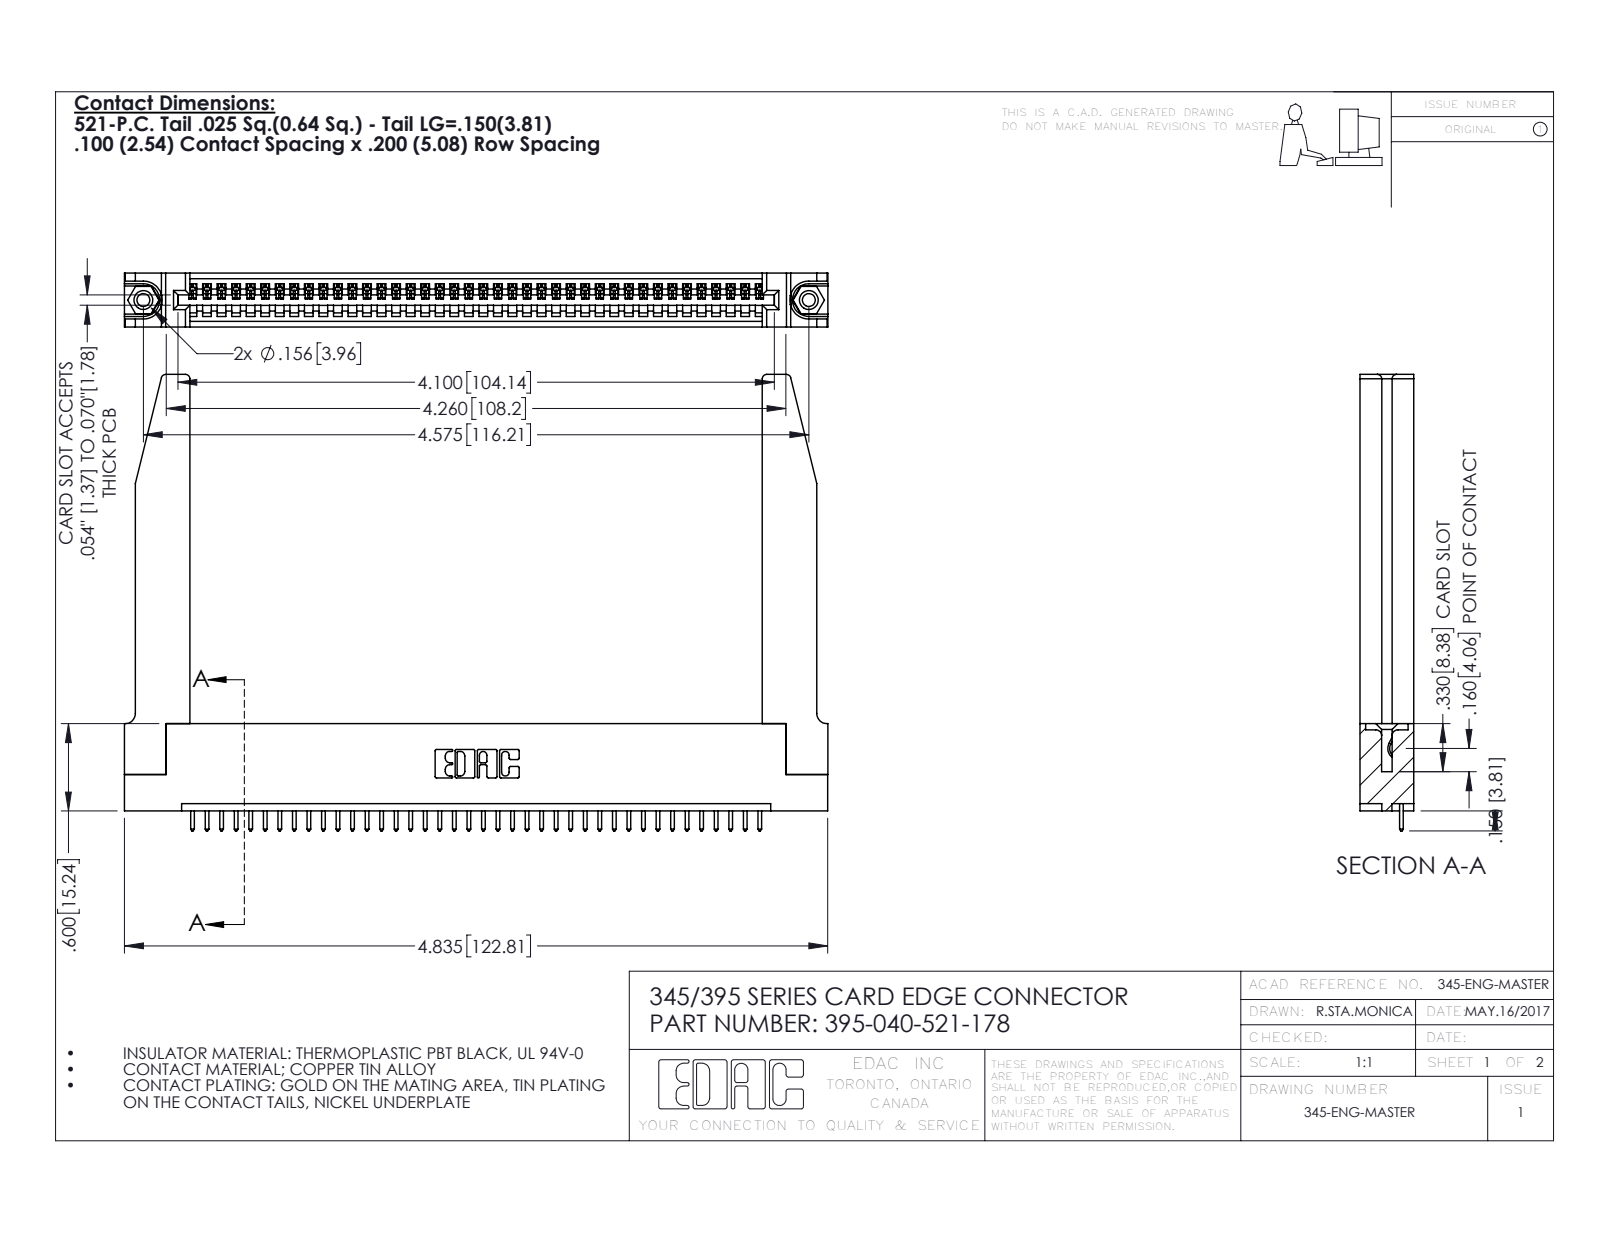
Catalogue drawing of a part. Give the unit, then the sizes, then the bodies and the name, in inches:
Units: inches
Overall size (bounding box): 4.836 × 3.137 × 0.37
Round holes (diameter × count): ⌀0.089 ×2, ⌀0.125 ×2, ⌀0.156 ×2, ⌀0.064 ×1
Round bosses / shafts (diameter × count): ⌀0.155 ×2
Partial cylindrical surfaces — rounded edges, fillets, slot ends (radius × count): R0.006 ×80, R0.01 ×80, R0.01 ×22, R0.03 ×8, R0.007 ×6, R0.031 ×6, R0.026 ×3, R0.031 ×2
Main face-to-face distances: 0.37, 0.072, 0.298, 0.2, 0.098, 0.272, 0.025, 0.225, 0.148, 0.15
Hole centre spacings: 0.27, 4.339, 4.575
Volume: 1.178 in³ · Surface area: 33.64 in²
Bodies: 45 solids, 2680 faces (1822 planar, 806 cylindrical, 52 other)
Part name (STEP PRODUCT): 345-220-078_345-220-078; 345 Part_Flush Mounting Lugs - 0.156 Dia-TH; 345-250-001_345-250-001-102; 395-040-521-178 (+1 more)
STEP written by: SolidWorks 2016 (CONFIG_CONTROL_DESIGN)
